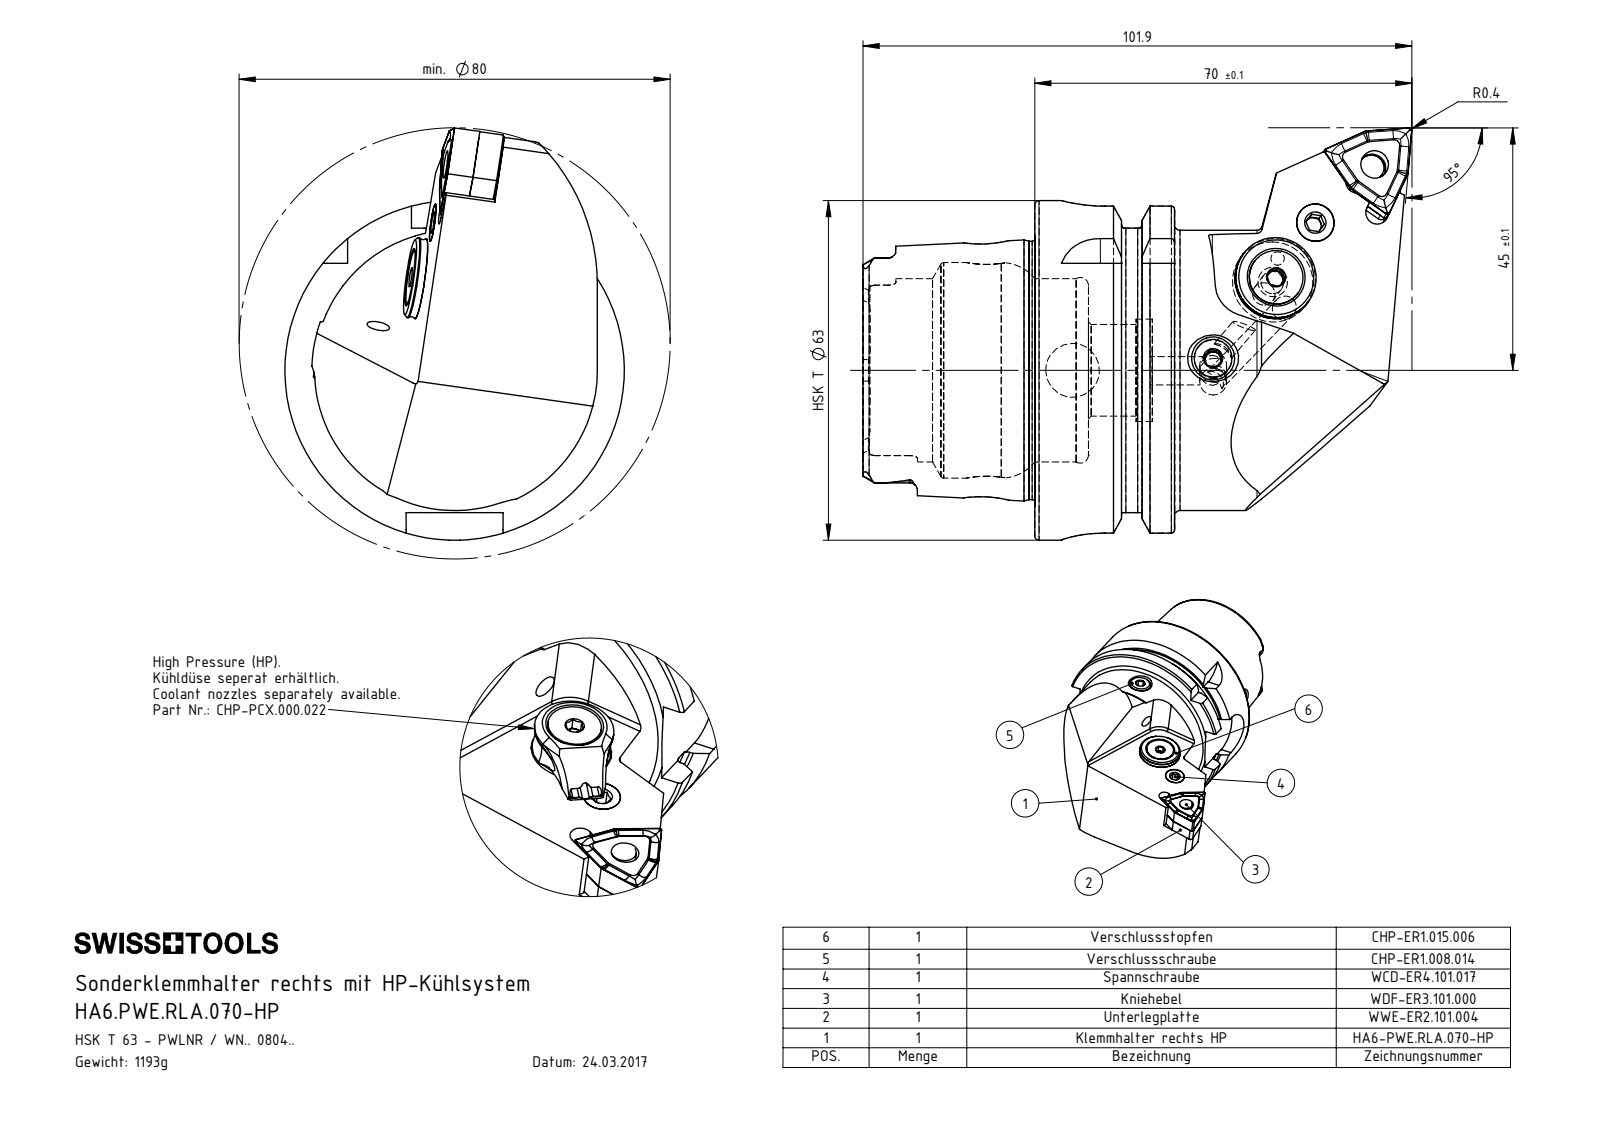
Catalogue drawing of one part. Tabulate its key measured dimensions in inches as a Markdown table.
| quantity | value |
| --- | --- |
| part name | DIN 3771 - 6.5x1.5; WWE-ER2.101.004_A; WNMG080404; CHP-ER1.008.014_A (+8 more) |
| STEP written by | SolidWorks 2017 (AUTOMOTIVE_DESIGN) |
| units | inches |
| bodies | 12 solids, 622 faces (181 planar, 171 cylindrical, 270 other) |
| overall size | 4.012 × 3.012 × 2.48 |
| volume | 9.265 in³ |
| surface area | 57.14 in² |
| round holes (diameter × count) | 0.165 × 3, 0.276 × 2, 0.331 × 2, 0.047 × 1, 0.079 × 1, 0.118 × 1, 0.197 × 1, 0.203 × 1, 0.209 × 1, 0.264 × 1, 0.295 × 1, 0.307 × 1 |
| round bosses / shafts (diameter × count) | 0.315 × 2, 2.48 × 1, 2.163 × 1, 2.047 × 1, 1.887 × 1, 0.585 × 1, 0.528 × 1, 0.394 × 1 |
| partial cylindrical surfaces (radius × count) | 0.039 × 10, 0.055 × 6, 0.113 × 4, 0.236 × 4, 0.315 × 4, 0.016 × 3, 0.098 × 3, 0.02 × 2 |
| main face-to-face distances | 1.022, 0.63, 0.392, 1.256, 1.648, 2.278, 2.079, 0.858, 0.187, 0.467 |
| hole center spacings | 1.122, 0.177, 0.177, 0.512, 0.614, 0.97, 0.971, 0.176 |
